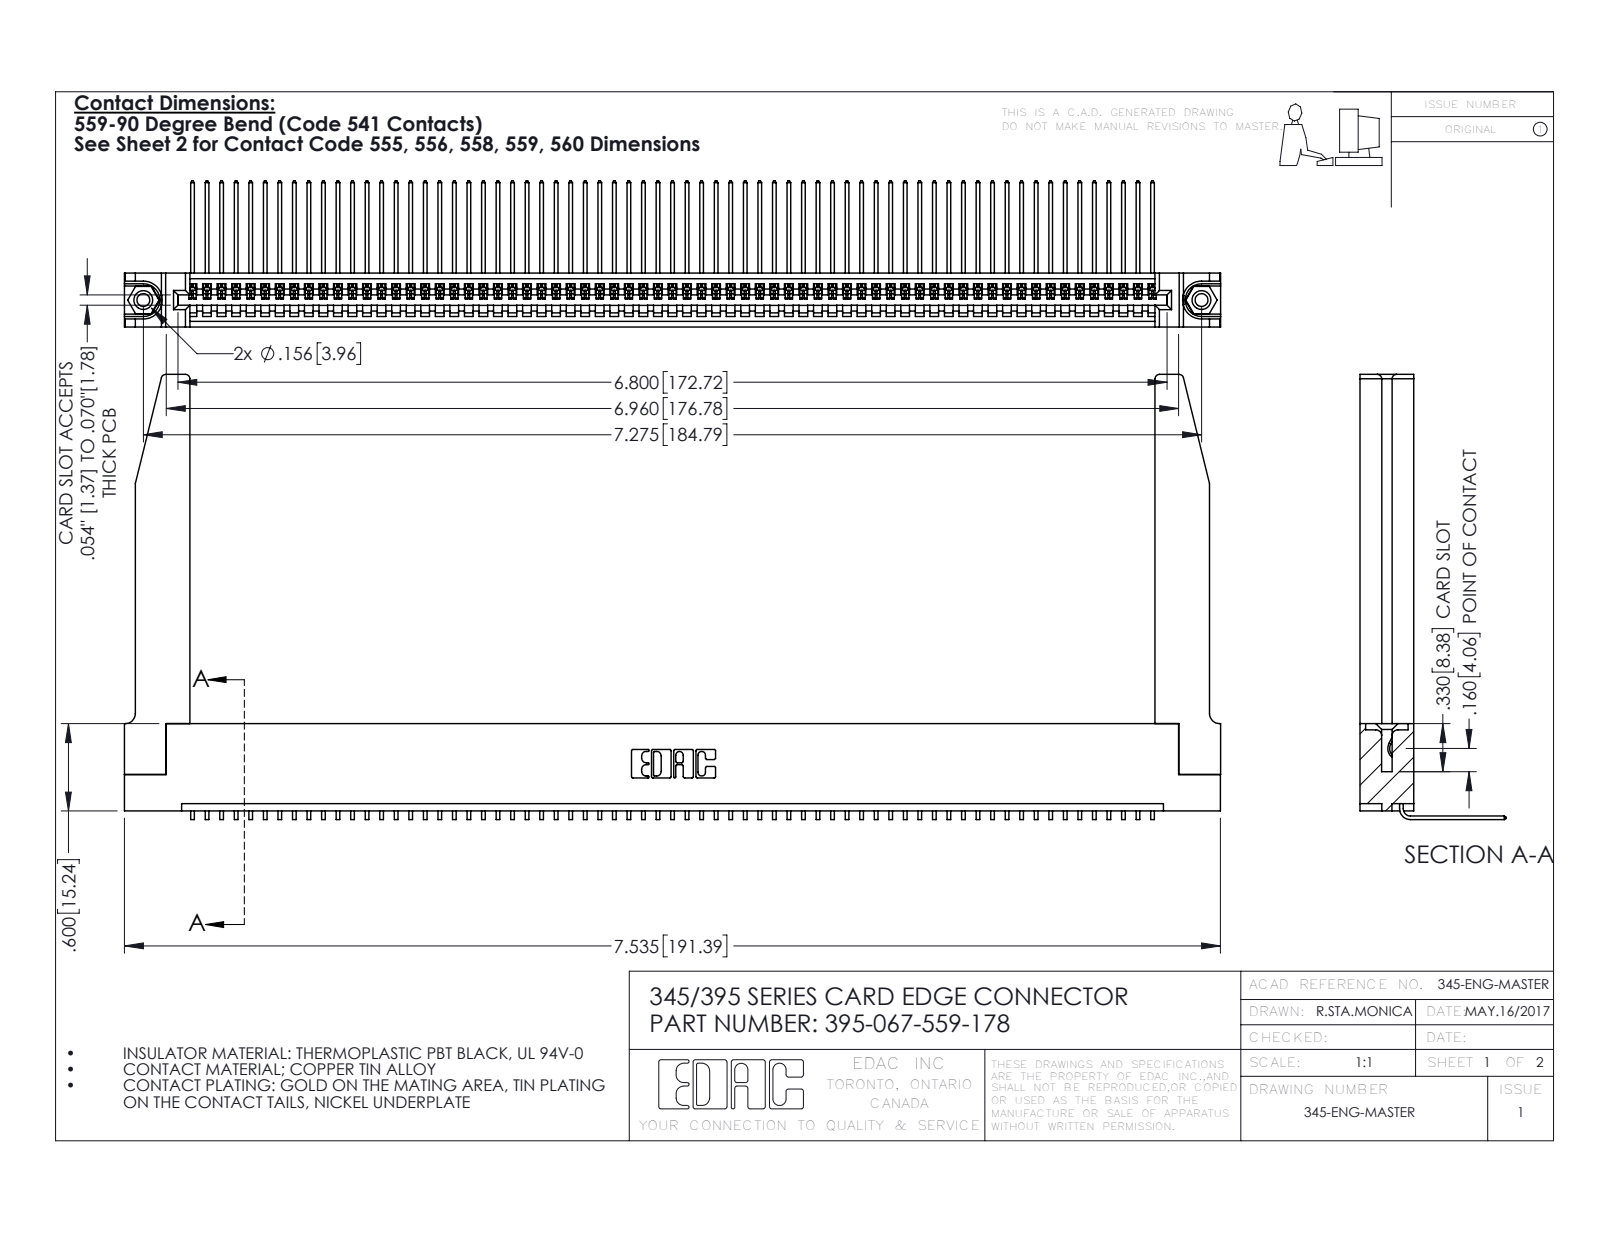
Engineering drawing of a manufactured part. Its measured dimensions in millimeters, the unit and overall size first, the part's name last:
Units: millimetres
Overall size (bounding box): 191.4 × 77.7 × 25.5
Round holes (diameter × count): ⌀2.3 ×2, ⌀3.2 ×2, ⌀4 ×2, ⌀1.6 ×1
Round bosses / shafts (diameter × count): ⌀3.9 ×2
Partial cylindrical surfaces — rounded edges, fillets, slot ends (radius × count): R0.2 ×134, R0.3 ×22, R0.8 ×8, R0.2 ×6, R0.8 ×6, R0.7 ×3, R0.8 ×2, R1 ×2
Main face-to-face distances: 9.4, 1.8, 7.6, 5.1, 2.5, 6.9, 0.6, 5.7, 3.8, 3.8
Hole centre spacings: 6.9, 178.8, 184.8
Volume: 26 380 mm³ · Surface area: 33 230 mm²
Bodies: 72 solids, 4380 faces (3036 planar, 1292 cylindrical, 52 other)
Part name (STEP PRODUCT): 345-220-078_345-220-078; 345-250-001_345-250-001-102; 345 Part_Flush Mounting Lugs - 0.156 Dia-TH; 345-292-001_558 559 Tail - 1 (+1 more)
STEP written by: SolidWorks 2016 (CONFIG_CONTROL_DESIGN)
